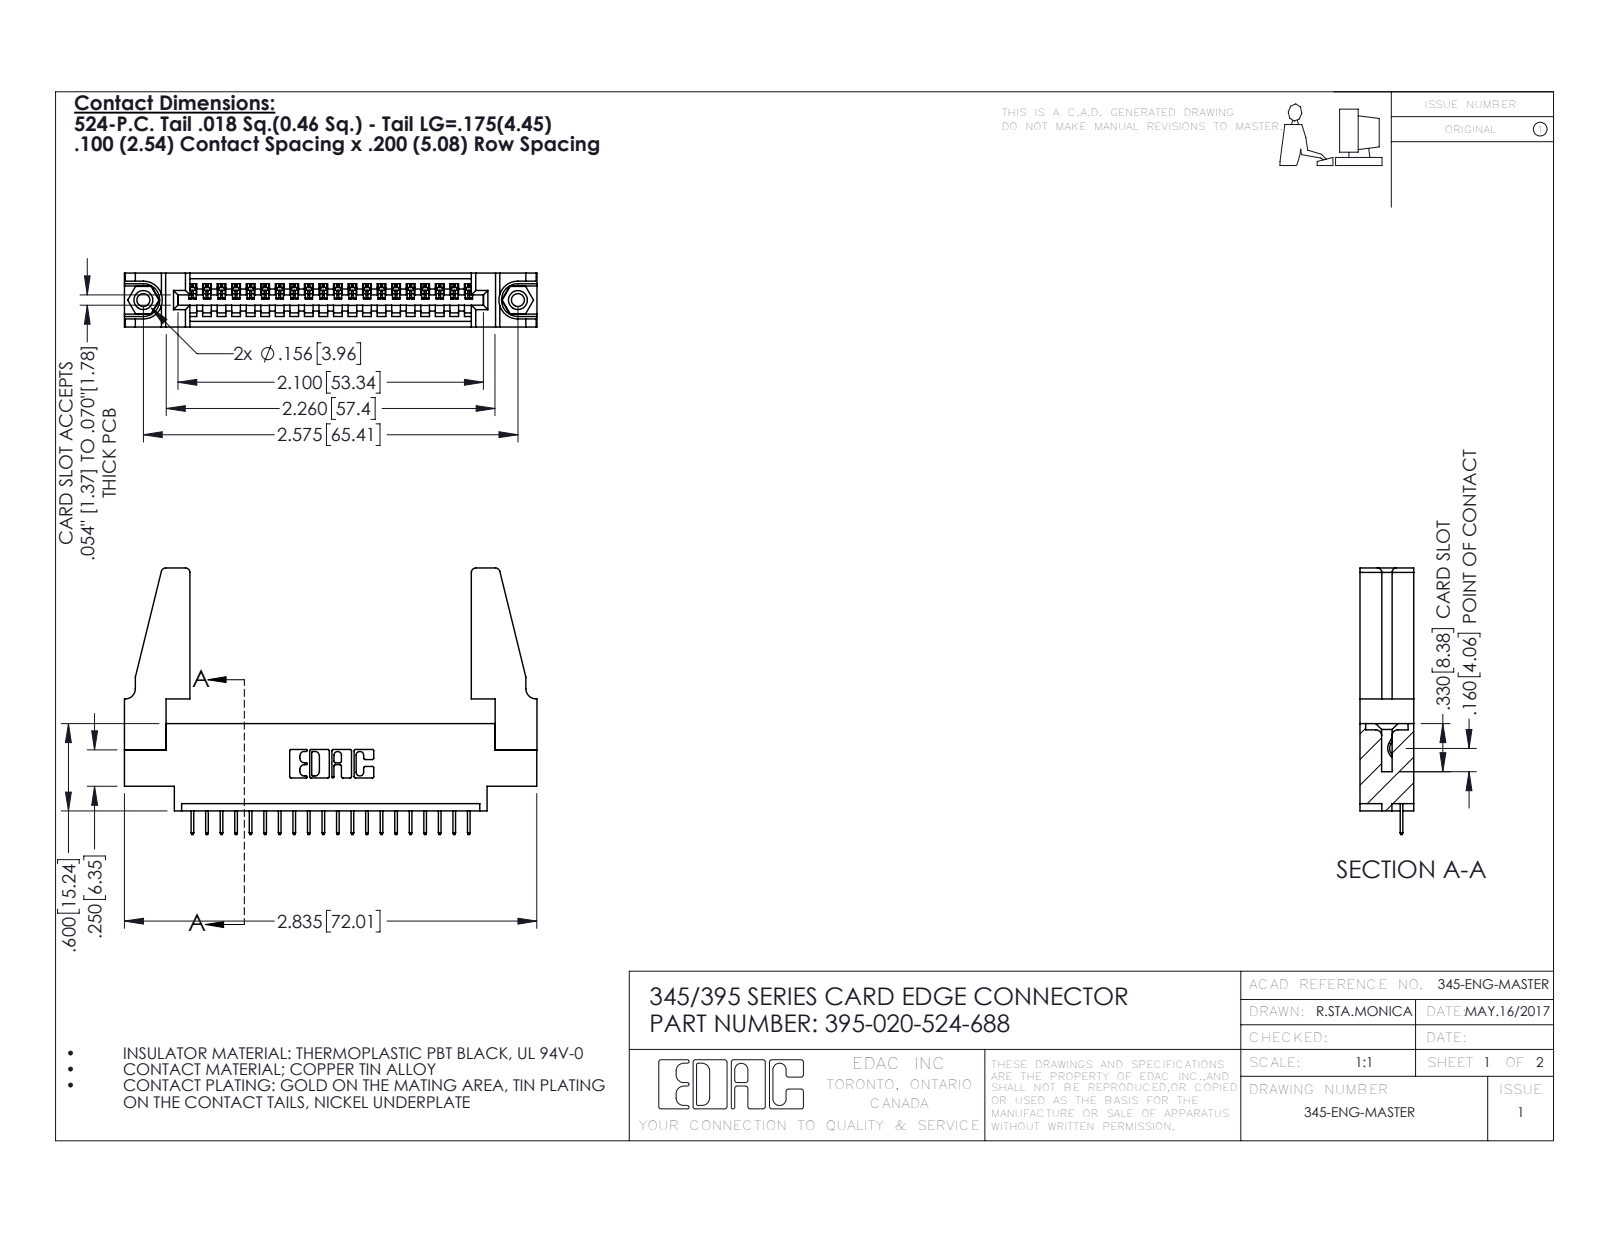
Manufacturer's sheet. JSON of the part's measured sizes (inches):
{"part_name": "345-220-078_345-220-088; 395-020-524-688; 345-292-001_345-293-124; 345-250-001_345-250-001-102 (+1 more)", "step_written_by": "SolidWorks 2016 (CONFIG_CONTROL_DESIGN)", "units": "inches", "bodies": {"solids": 25, "faces": 1494, "planar": 1076, "cylindrical": 402, "other": 16}, "overall_size": [2.836, 1.832, 0.37], "volume_in3": 0.593, "surface_area_in2": 17.52, "round_holes": [[0.089, 2], [0.125, 2], [0.156, 2], [0.064, 1]], "round_bosses_or_shafts": [[0.155, 2]], "partial_cylinders_radius": [[0.006, 40], [0.01, 22], [0.03, 8], [0.007, 6], [0.031, 6], [0.026, 3], [0.031, 2], [0.04, 2]], "face_to_face_distances": [0.37, 0.072, 0.298, 0.2, 0.098, 0.272, 0.025, 0.225, 0.072, 0.175], "hole_center_spacings": [0.27, 2.341, 2.575]}
